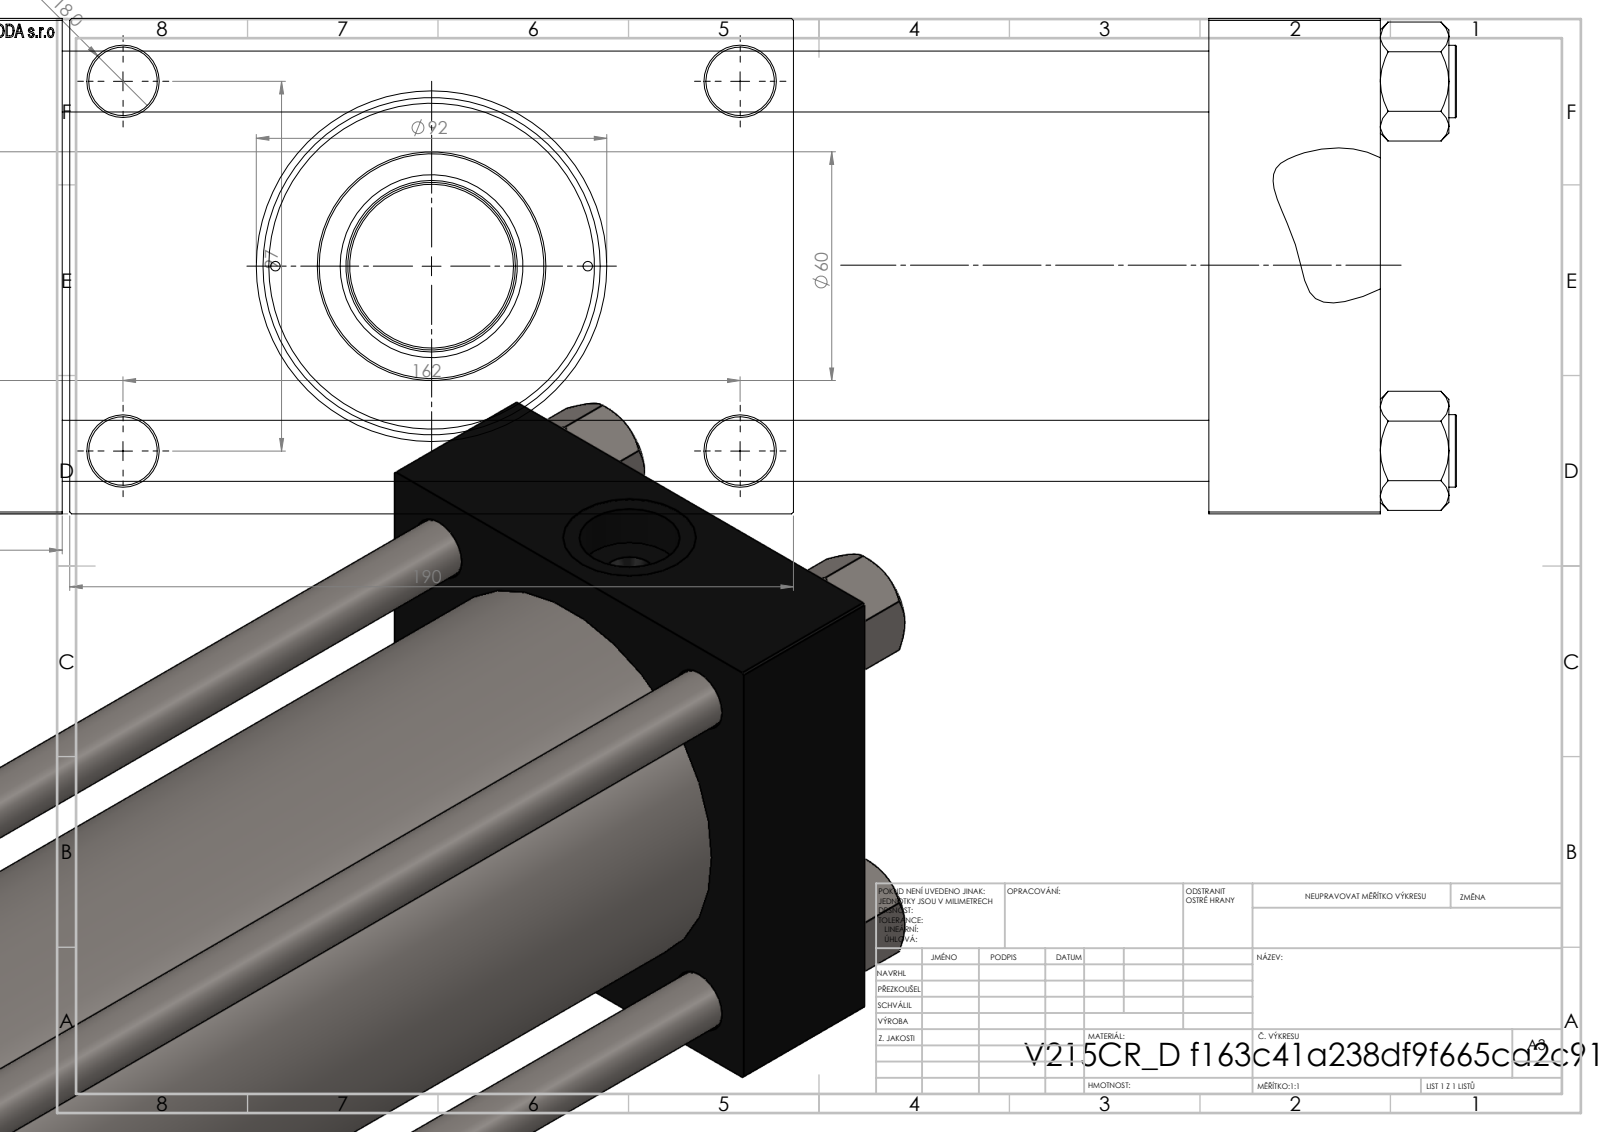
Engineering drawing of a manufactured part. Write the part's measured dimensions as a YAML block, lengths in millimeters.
part_name: "V215_VC_A; V215CR_ROD_END_F; V215CR_D_TYCINKA; V215CR_VCP_D (+2 more)"
step_written_by: "SolidWorks 2019 (CONFIG_CONTROL_DESIGN)"
units: millimeters
bodies: {solids: 12, faces: 1173, planar: 550, cylindrical: 97, other: 526}
overall_size: [517, 190, 130]
volume: 3433000
surface_area: 588226
round_holes:
  - {diameter: 16, count: 4}
  - {diameter: 18, count: 4}
  - {diameter: 2.5, count: 2}
  - {diameter: 7, count: 2}
  - {diameter: 26.44, count: 2}
  - {diameter: 35, count: 2}
  - {diameter: 31.5, count: 1}
  - {diameter: 45, count: 1}
  - {diameter: 48, count: 1}
  - {diameter: 76, count: 1}
  - {diameter: 85.5, count: 1}
  - {diameter: 100, count: 1}
round_bosses_or_shafts:
  - {diameter: 19, count: 4}
  - {diameter: 106, count: 1}
  - {diameter: 92, count: 1}
  - {diameter: 60, count: 1}
  - {diameter: 44, count: 1}
  - {diameter: 33, count: 1}
face_to_face_distances: [130, 45, 346, 301, 396, 351, 50, 30, 160, 190]
hole_center_spacings: [32.55, 49.02, 62.87, 68.52, 94.41, 96.9, 101.73, 102.27]
